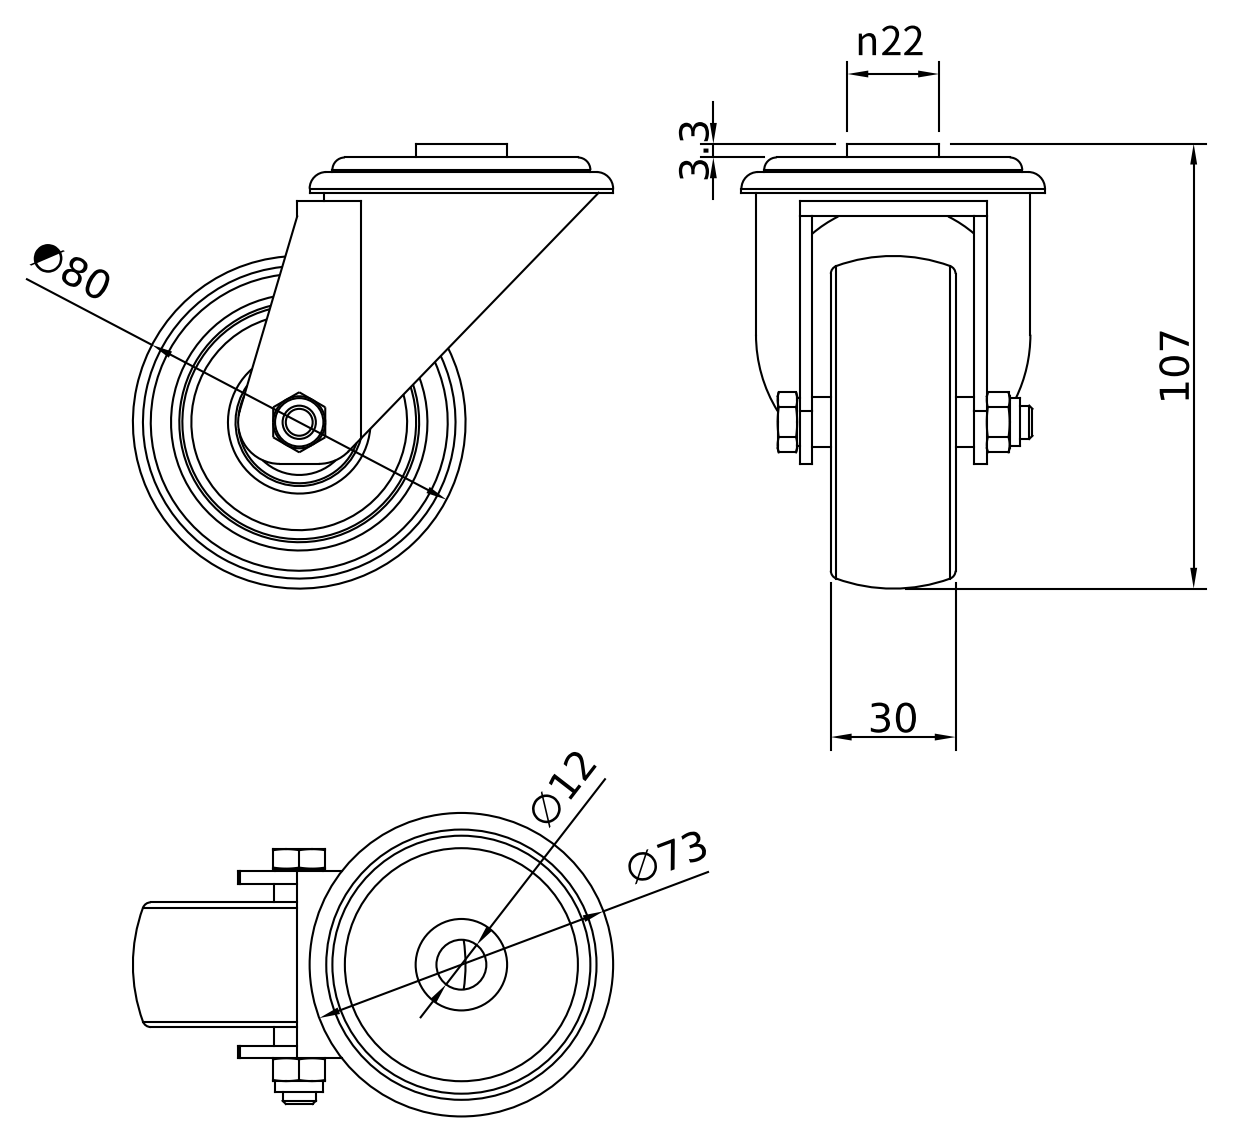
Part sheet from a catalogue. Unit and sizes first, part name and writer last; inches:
Units: inches
Overall size (bounding box): 4.547 × 4.213 × 2.874
Round holes (diameter × count): ⌀0.472 ×2, ⌀0.354 ×1, ⌀2.402 ×1
Round bosses / shafts (diameter × count): ⌀2.874 ×1, ⌀2.598 ×1, ⌀2.443 ×1, ⌀0.866 ×1, ⌀0.458 ×1, ⌀0.315 ×1
Partial cylindrical surfaces — rounded edges, fillets, slot ends (radius × count): R0.394 ×2
Main face-to-face distances: 0.118, 1.654, 0.295, 1.476, 0.177, 1.358, 0.421, 1.772, 1.535, 1.181
Volume: 9.762 in³ · Surface area: 77.15 in²
Bodies: 3 solids, 106 faces (42 planar, 20 cylindrical, 44 other)
Part name (STEP PRODUCT): CRUST0000201; 440000025916; 440000025915; 440000025914
STEP written by: Autodesk Inventor 2022 (AUTOMOTIVE_DESIGN)
